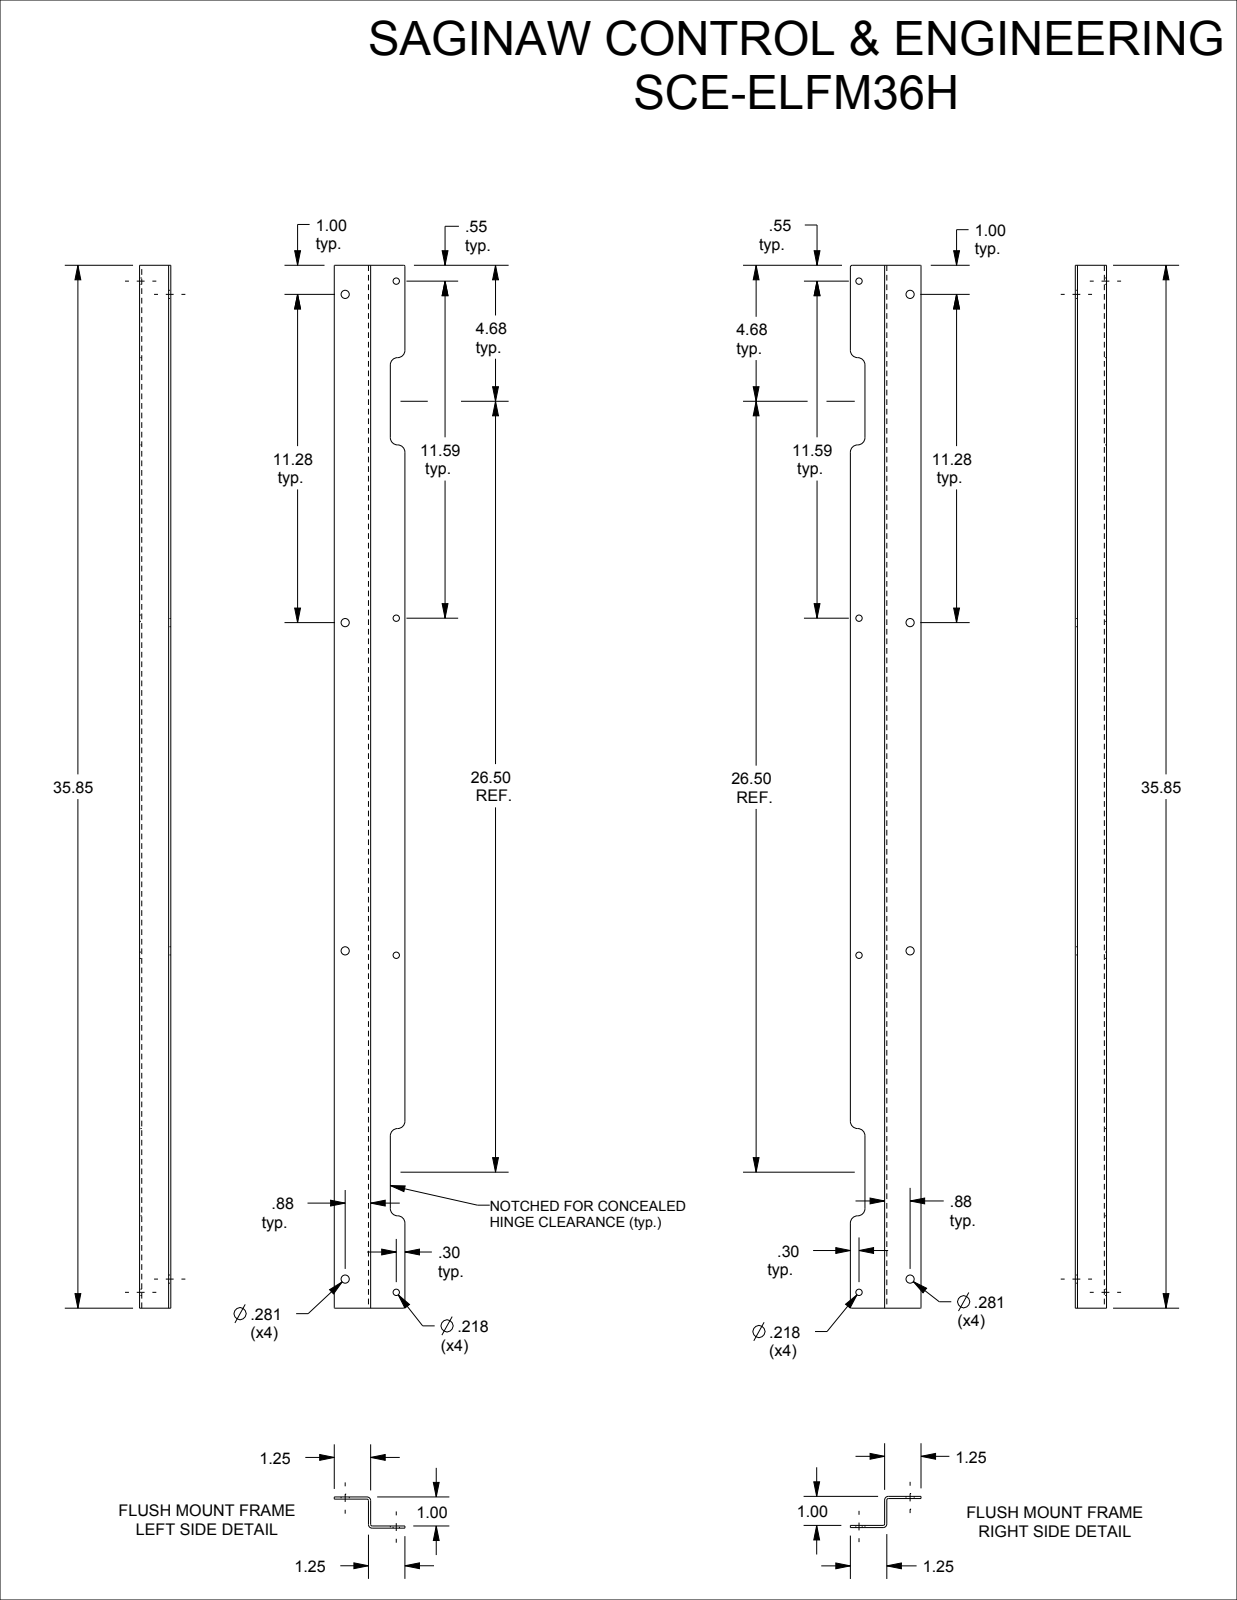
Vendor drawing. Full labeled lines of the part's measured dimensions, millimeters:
Part name (STEP PRODUCT): SCE-ELFM36H
STEP written by: SolidWorks 2019 (CONFIG_CONTROL_DESIGN)
Units: millimetres
Bodies: 2 solids, 84 faces (36 planar, 48 cylindrical, 0 other)
Overall size (bounding box): 910.6 × 685.8 × 27.3
Volume: 286 800 mm³ · Surface area: 309 400 mm²
Round holes (diameter × count): ⌀5.5 ×8, ⌀7.1 ×8
Partial cylindrical surfaces — rounded edges, fillets, slot ends (radius × count): R6.4 ×16, R0.4 ×4, R1.3 ×4, R3.2 ×4, R1 ×2, R1.6 ×2
Main face-to-face distances: 1.9, 1.9, 25.3, 27.3, 23.4, 25.3, 624.2, 626.1, 622.3, 624.2
Hole centre spacings: 294.3, 648.3, 44.8, 46.1, 286.2, 286.6, 293.9, 301.5
